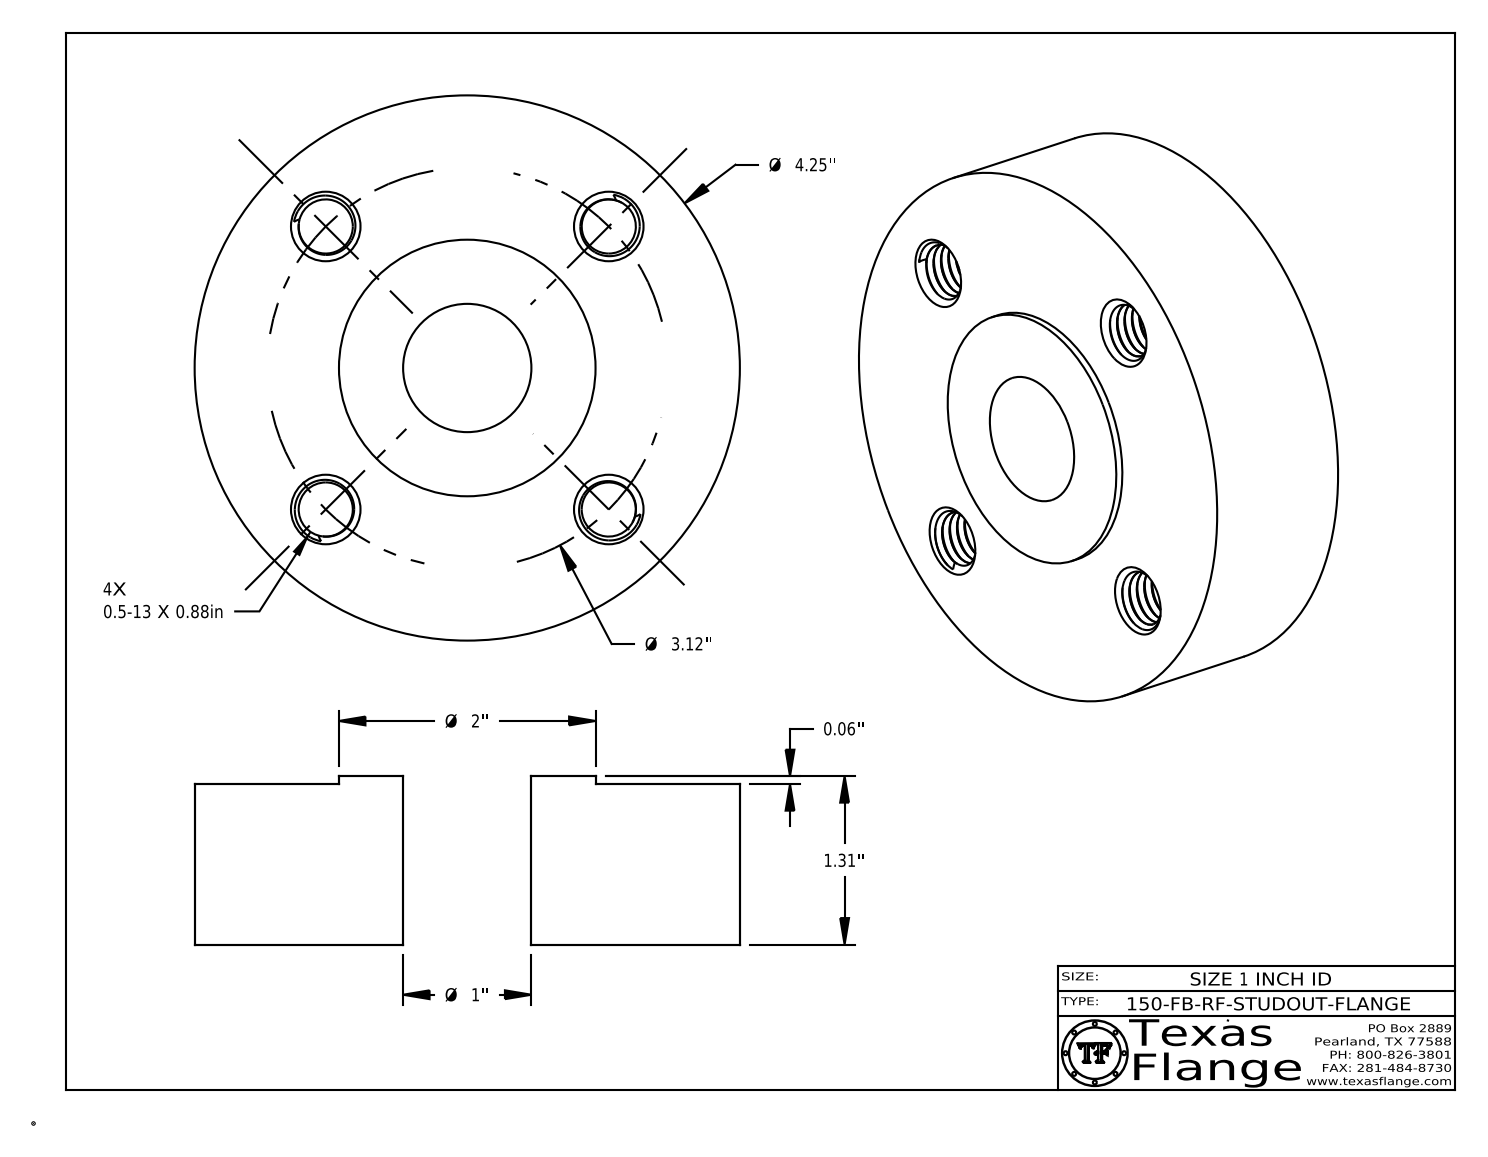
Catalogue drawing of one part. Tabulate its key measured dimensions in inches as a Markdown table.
| quantity | value |
| --- | --- |
| part name | 1-150-FB-RF-STUDOUT-FLANGE |
| STEP written by | CATIA V5 STEP AP214 (AUTOMOTIVE_DESIGN) |
| units | inches |
| bodies | 1 solid, 586 faces (368 planar, 82 cylindrical, 136 other) |
| overall size | 4.25 × 4.25 × 1.313 |
| volume | 16.32 in³ |
| surface area | 54.19 in² |
| round holes (diameter × count) | 0.422 × 4, 1 × 2 |
| round bosses / shafts (diameter × count) | 0.061 × 8, 4.25 × 1, 2 × 1, 0.788 × 1 |
| main face-to-face distances | 1.25, 0.063, 1.313, 0.015, 1.298, 1.235, 0.298, 0.293, 0.054, 0.248 |
| hole center spacings | 1.56, 2.206, 1.194, 2.882, 3.12, 1.56 |
